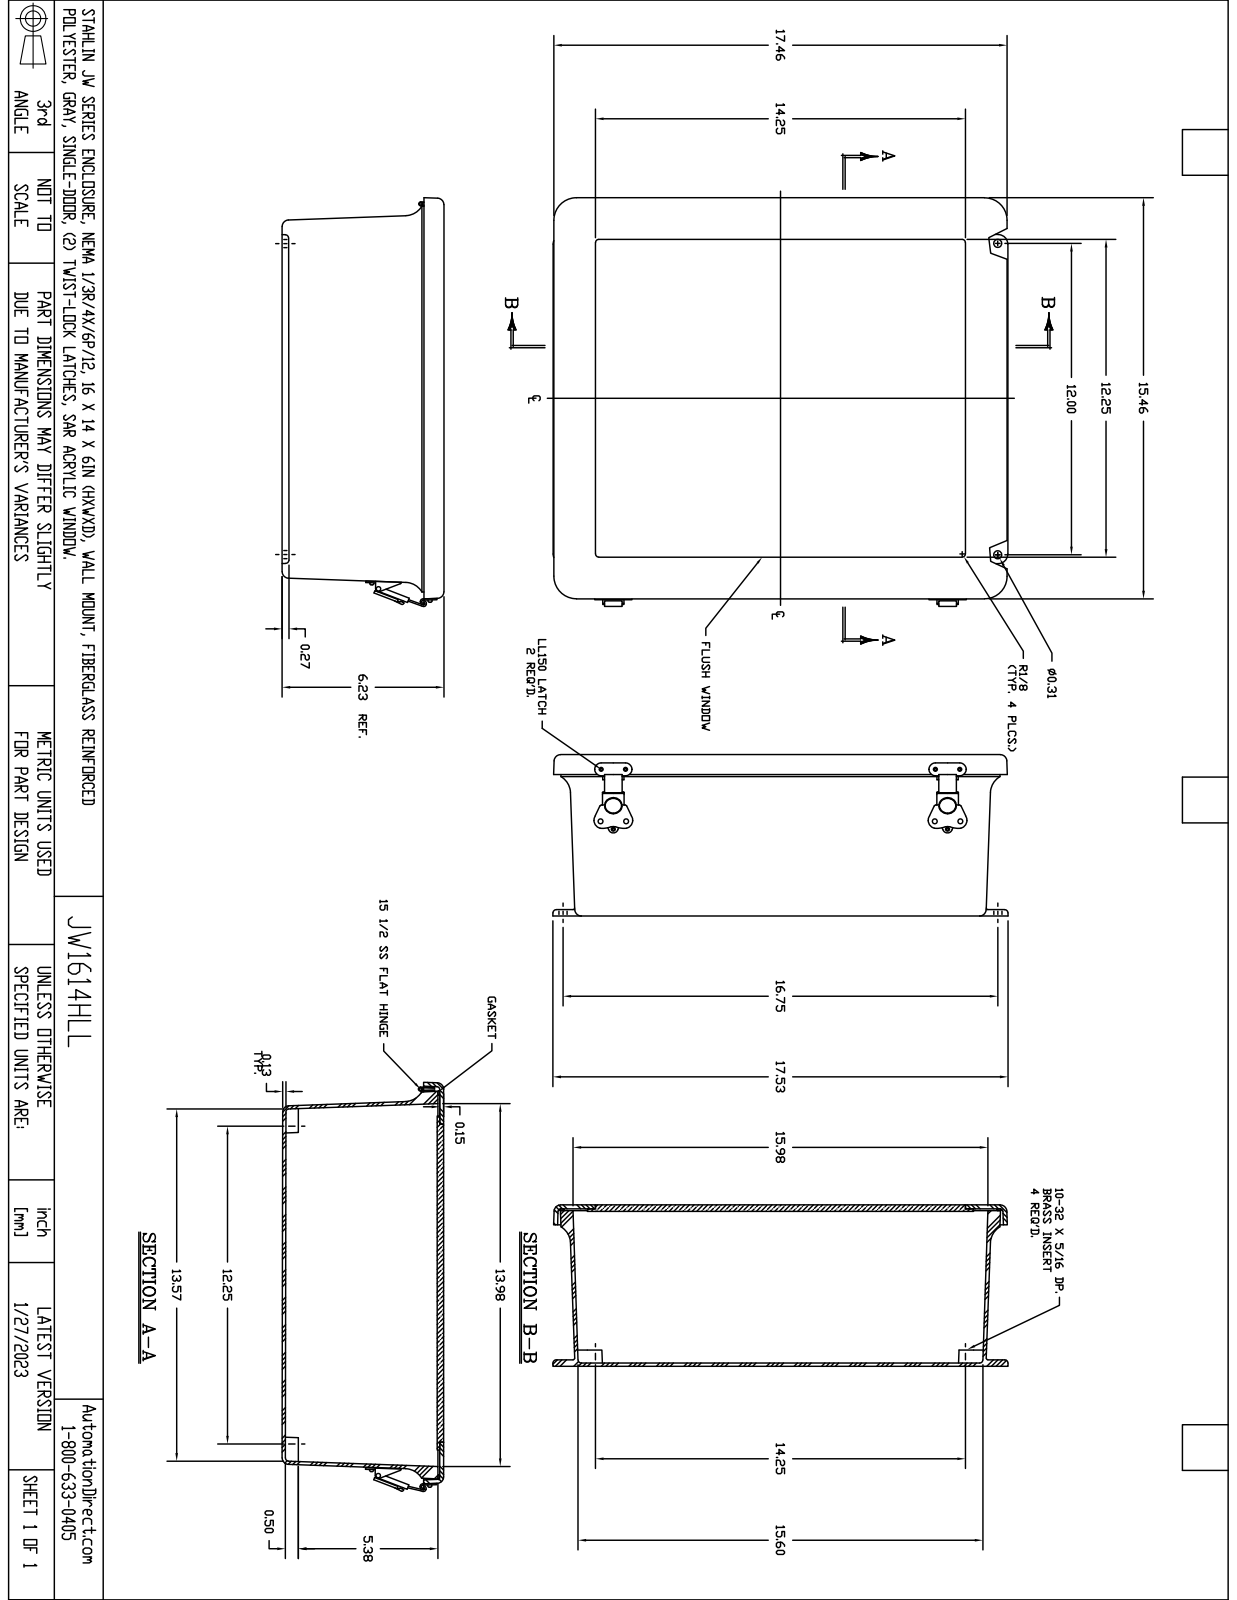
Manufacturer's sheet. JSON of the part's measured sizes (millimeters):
{"part_name": "MW1614HLL", "step_written_by": "SolidWorks 2018 (AUTOMOTIVE_DESIGN)", "units": "millimeters", "bodies": {"solids": 51, "faces": 1275, "planar": 582, "cylindrical": 500, "other": 193}, "overall_size": [445.3, 397.5, 157.7], "volume_mm3": 2671000, "surface_area_mm2": 1305000, "round_holes": [[3.6, 18], [3.3, 10], [3.9, 8], [3.3, 4], [4, 4], [4.2, 4], [5, 4], [5.5, 4], [3, 2], [3.5, 2], [4.6, 2], [4.6, 2]], "round_bosses_or_shafts": [[6.4, 18], [3.2, 11], [3.2, 7], [6.9, 4], [14.8, 2], [13.3, 2], [5.3, 2], [4.7, 2]], "partial_cylinders_radius": [[0.8, 20], [2, 19], [3.2, 16], [6.4, 16], [0.9, 8], [1, 8], [1.1, 8], [1.2, 8]], "face_to_face_distances": [3.2, 157.7, 6.4, 151.4, 154.5, 148.2, 3.9, 3.2, 153.8, 150.6], "hole_center_spacings": [95.3, 190.5, 326.8, 285.8, 326.9, 6.4, 88.9, 23.8]}
